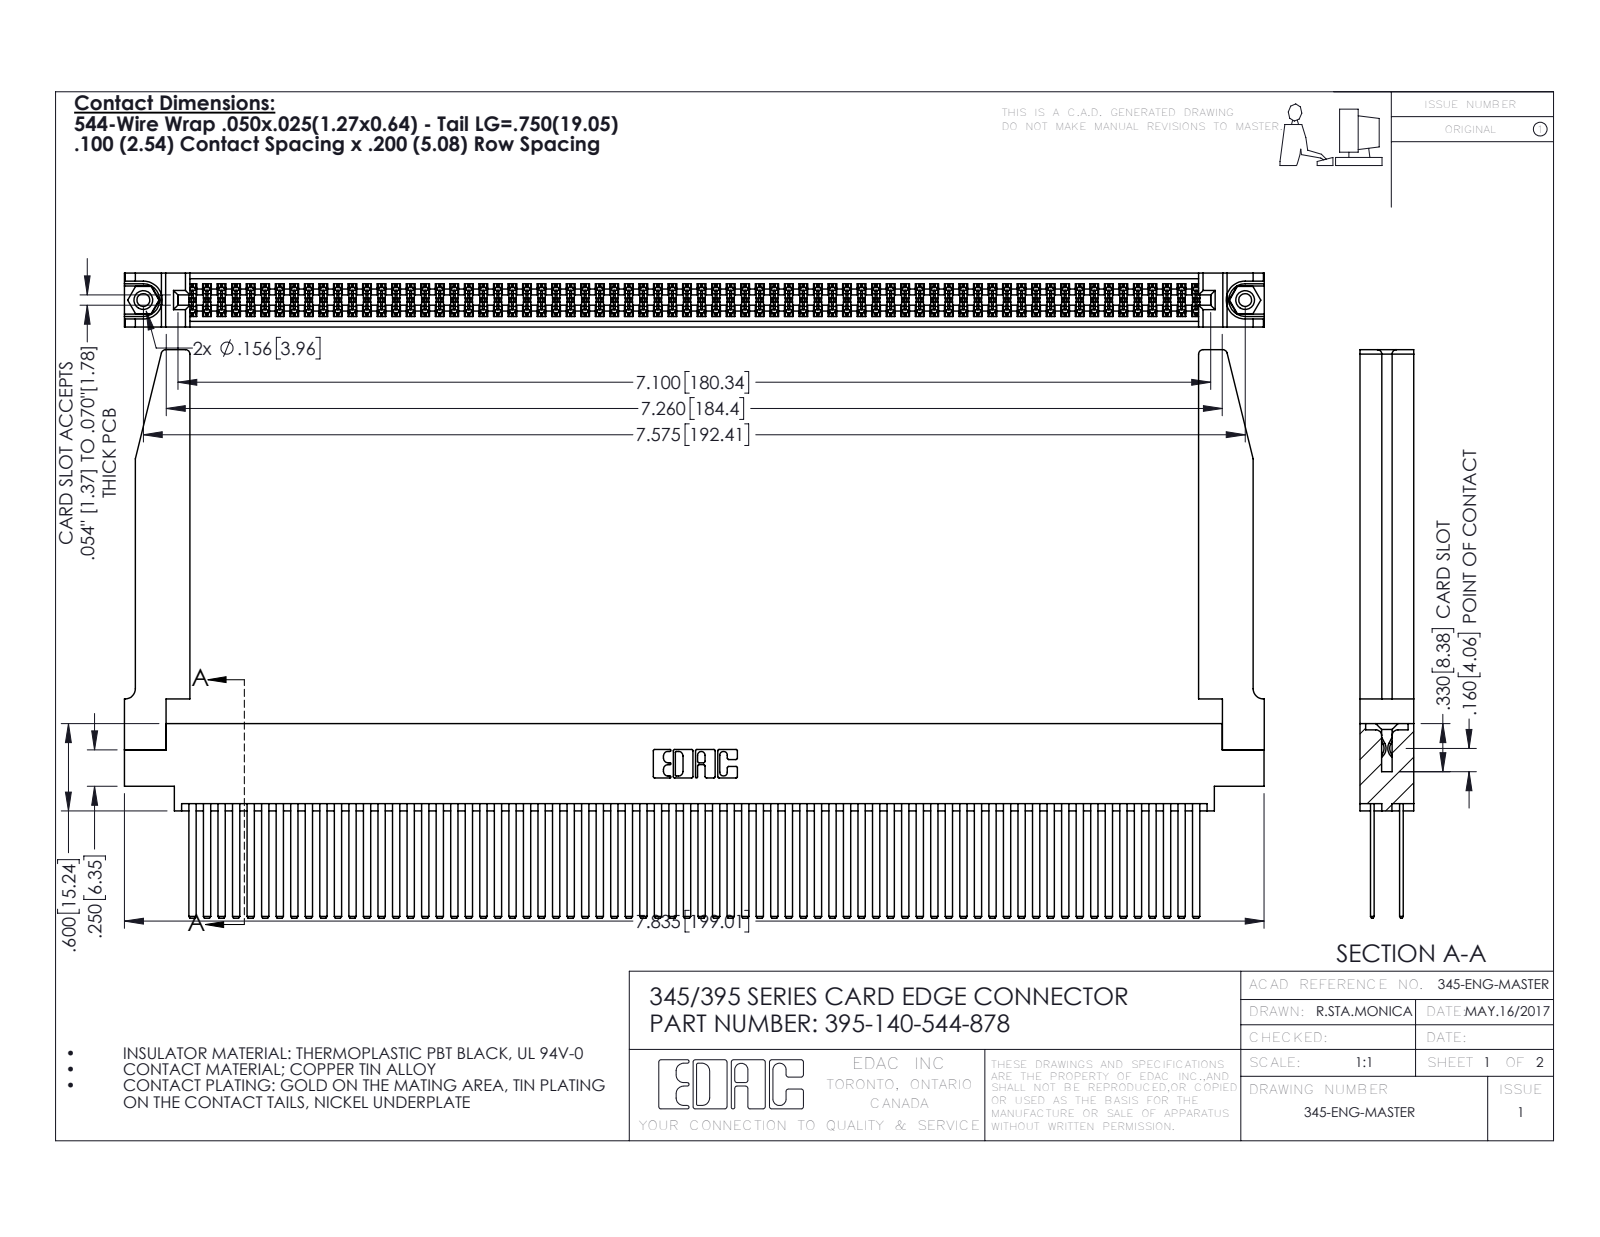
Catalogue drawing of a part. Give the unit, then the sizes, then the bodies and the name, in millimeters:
Units: millimetres
Overall size (bounding box): 199 × 99.2 × 9.4
Round holes (diameter × count): ⌀2.3 ×2, ⌀3.2 ×2, ⌀4 ×2, ⌀1.6 ×1
Round bosses / shafts (diameter × count): ⌀3.9 ×2
Partial cylindrical surfaces — rounded edges, fillets, slot ends (radius × count): R0.2 ×210, R0.3 ×22, R0.8 ×8, R0.2 ×6, R0.8 ×6, R0.7 ×3, R0.4 ×2, R0.5 ×2
Main face-to-face distances: 1.8, 7.6, 2.5, 6.9, 0.6, 5.1, 9.4, 5.7, 4.4, 3.8
Hole centre spacings: 6.9, 186.4, 192.4
Volume: 29 220 mm³ · Surface area: 44 970 mm²
Bodies: 145 solids, 6524 faces (4286 planar, 2186 cylindrical, 52 other)
Part name (STEP PRODUCT): 345 Part_0.170 Offset - 0.156 Dia-TH; 345-250-001_345-250-001-102; 345-292-001_345-293-144; 395-140-544-878 (+1 more)
STEP written by: SolidWorks 2016 (CONFIG_CONTROL_DESIGN)
